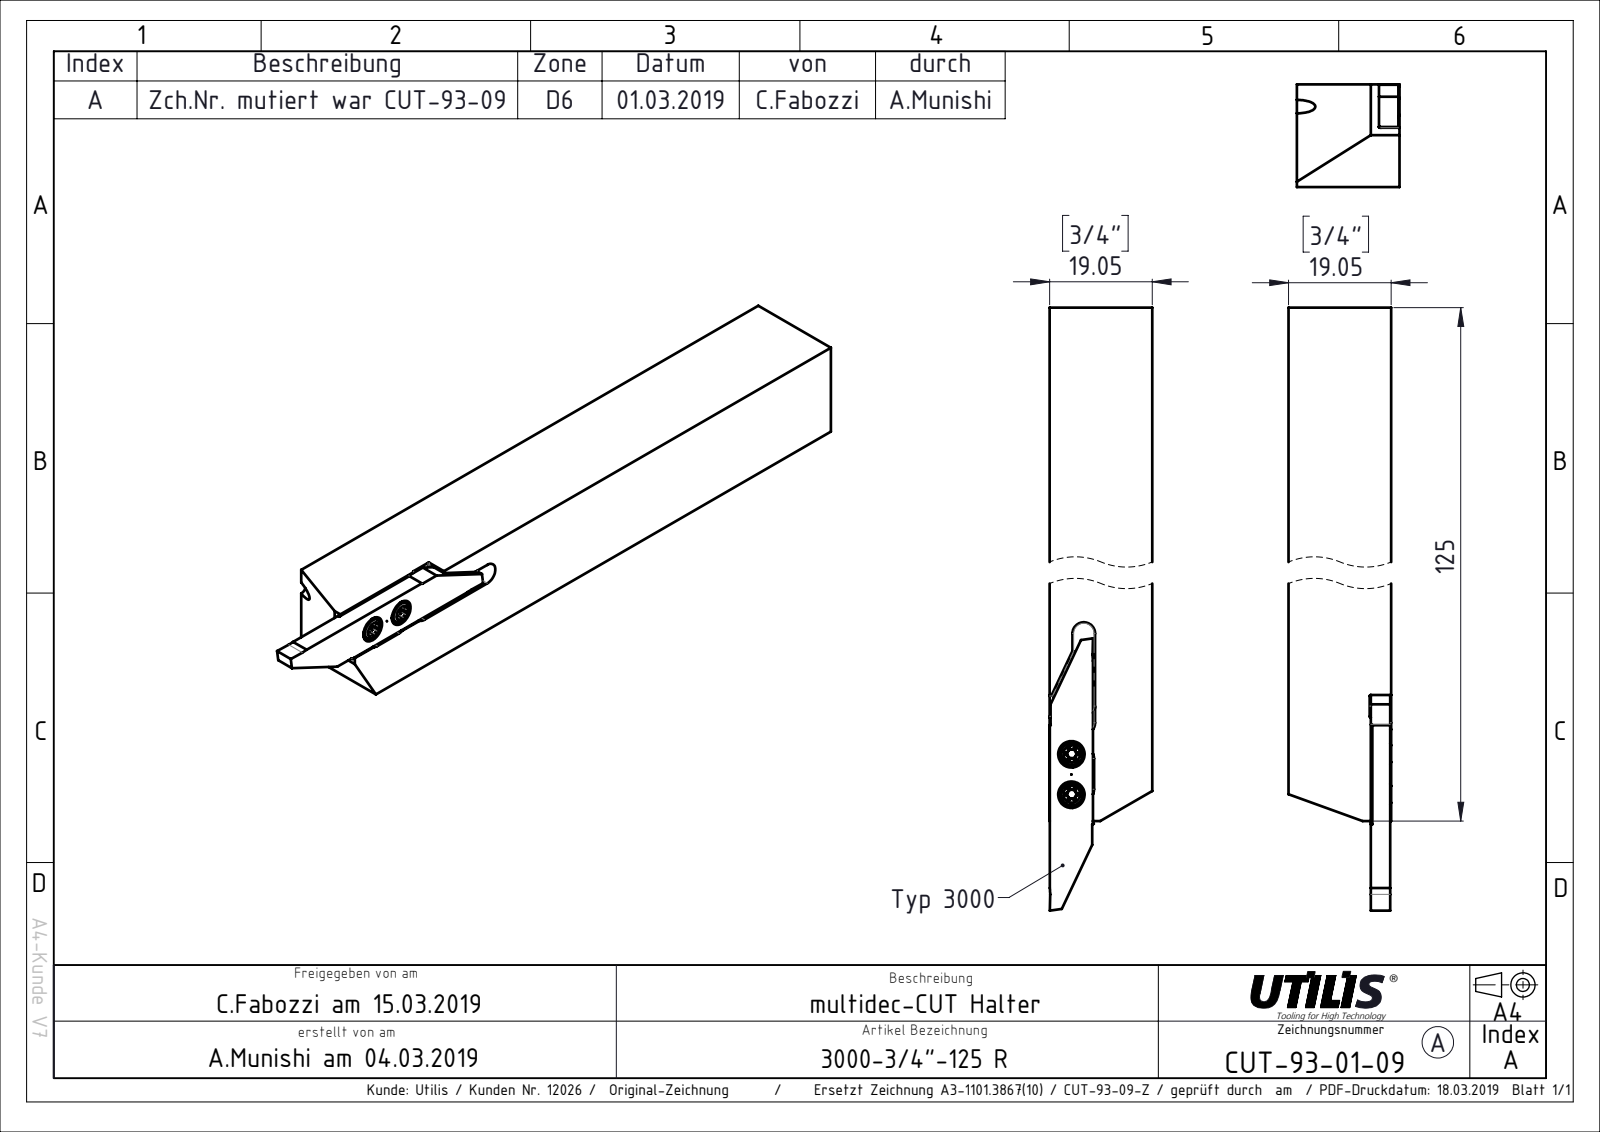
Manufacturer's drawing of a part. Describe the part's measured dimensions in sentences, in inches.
The part is named "CUT-Vorlage 3000 R+L Lang Kunde; CUT-93-Kunde; CUT-93-09; CUT-Vorlage 3000 R+L Lang Kunde_R-Lang (+1 more)". Its 3-D file was written by "SolidWorks 2015 (CONFIG_CONTROL_DESIGN)". It is 2 solids with 55 faces: 36 planar, 19 cylindrical and 0 other. Overall it measures 5.571 by 0.75 by 0.75 inches. Its volume is 2.705 cubic inches and its surface area 17.65 square inches. Round holes: 2 of diameter 0.098, 2 of diameter 0.193. Partial cylindrical surfaces (rounded edges, fillets, slot ends): 4 of radius 0.083, 2 of radius 0.006, 2 of radius 0.394. The main face-to-face distances are 0.75, 0.15, 0.6, 0.142, 0.742, 0.435, 0.315, 0.417, 0.018, 0.333. The hole center spacings are 0.148, 0.295.
